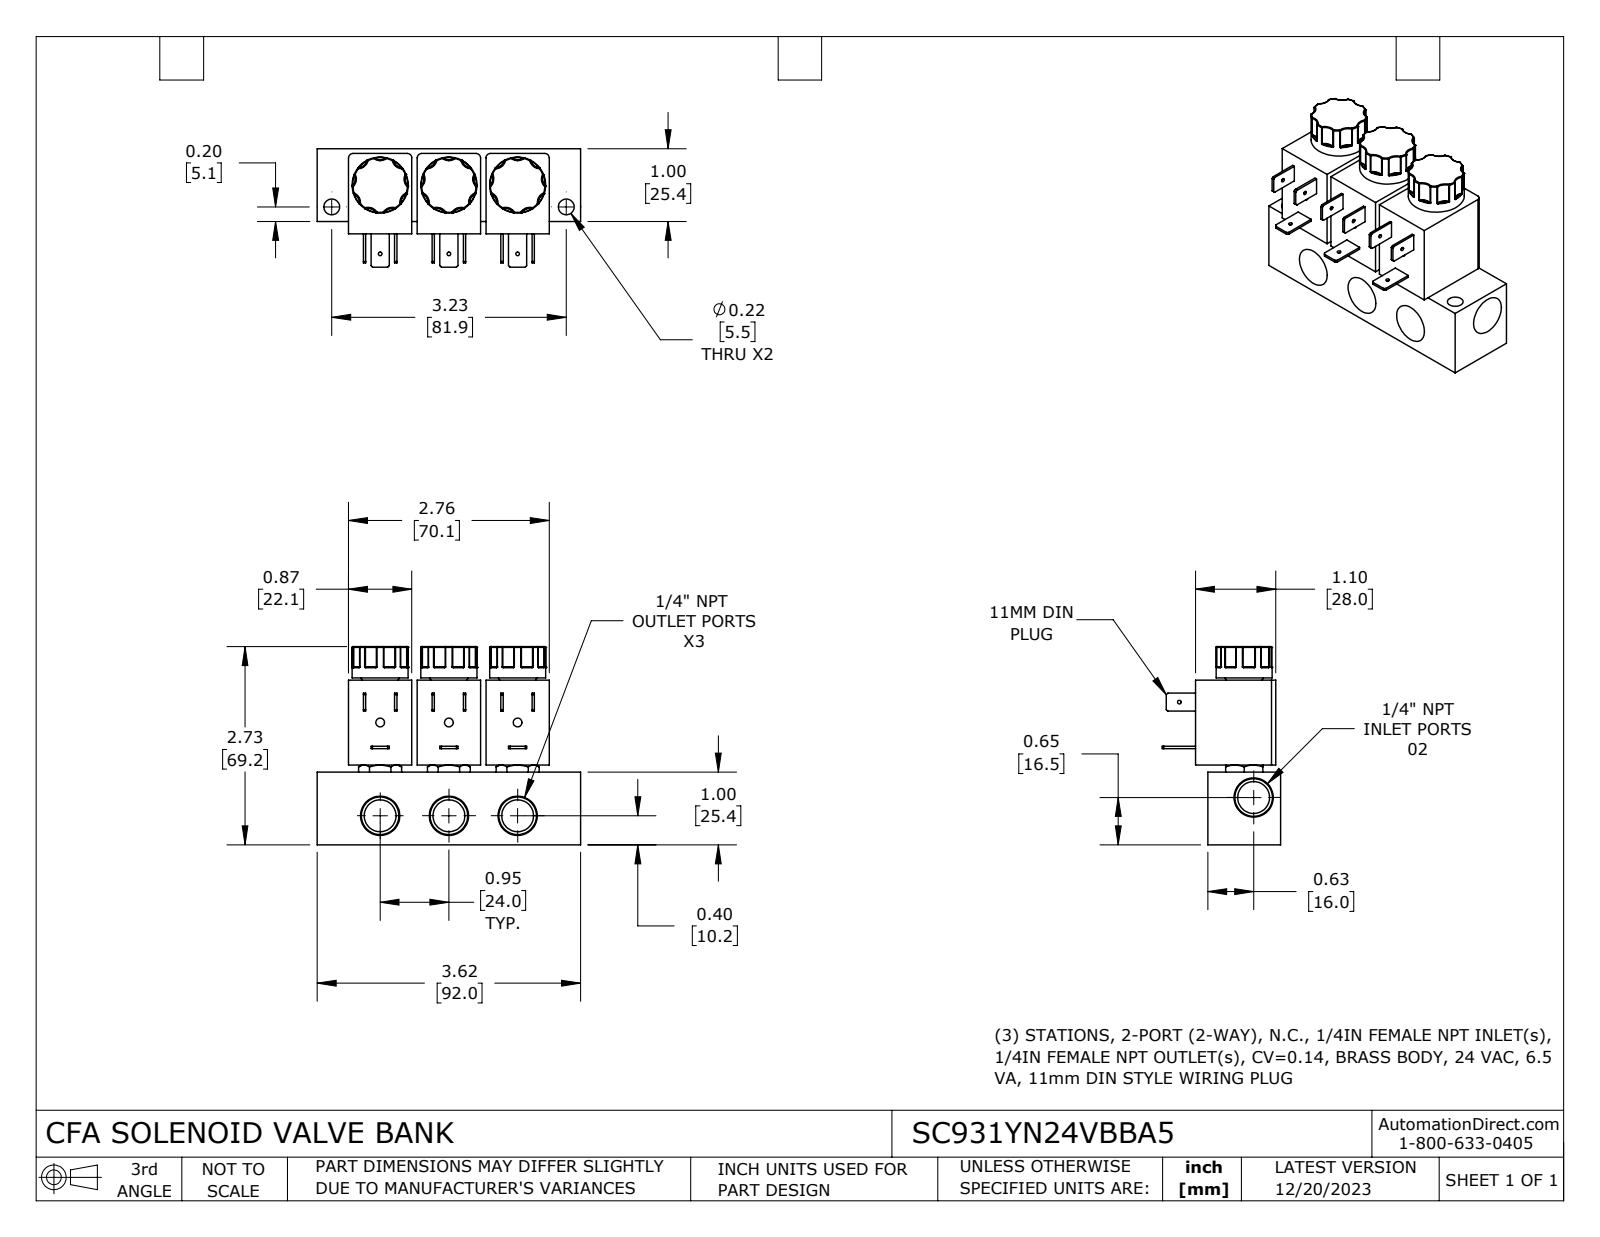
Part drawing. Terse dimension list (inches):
name: SC931YN24VBBA5
written by: SolidWorks 2023 (CONFIG_CONTROL_DESIGN)
unit: in
bodies: 1 solid, 657 faces (146 planar, 140 cylindrical, 371 other)
size: 3.622 × 2.725 × 1.627
volume: 7.008 in³; area: 47.81 in²
holes: 4× ⌀0.05, 4× ⌀0.438, 3× ⌀0.12, 2× ⌀0.217
bosses: 3× ⌀0.77
rounds: 54× R0.01, 25× R0.133, 6× R0.06, 2× R0.132
face distances: 1, 0.945, 0.87, 1.169, 0.169, 0.065, 0.935, 1.104, 1.89, 1.815
hole spacings: 0.945, 1.593, 1.282, 1.89, 2.283, 0.928, 0.93, 1.662
